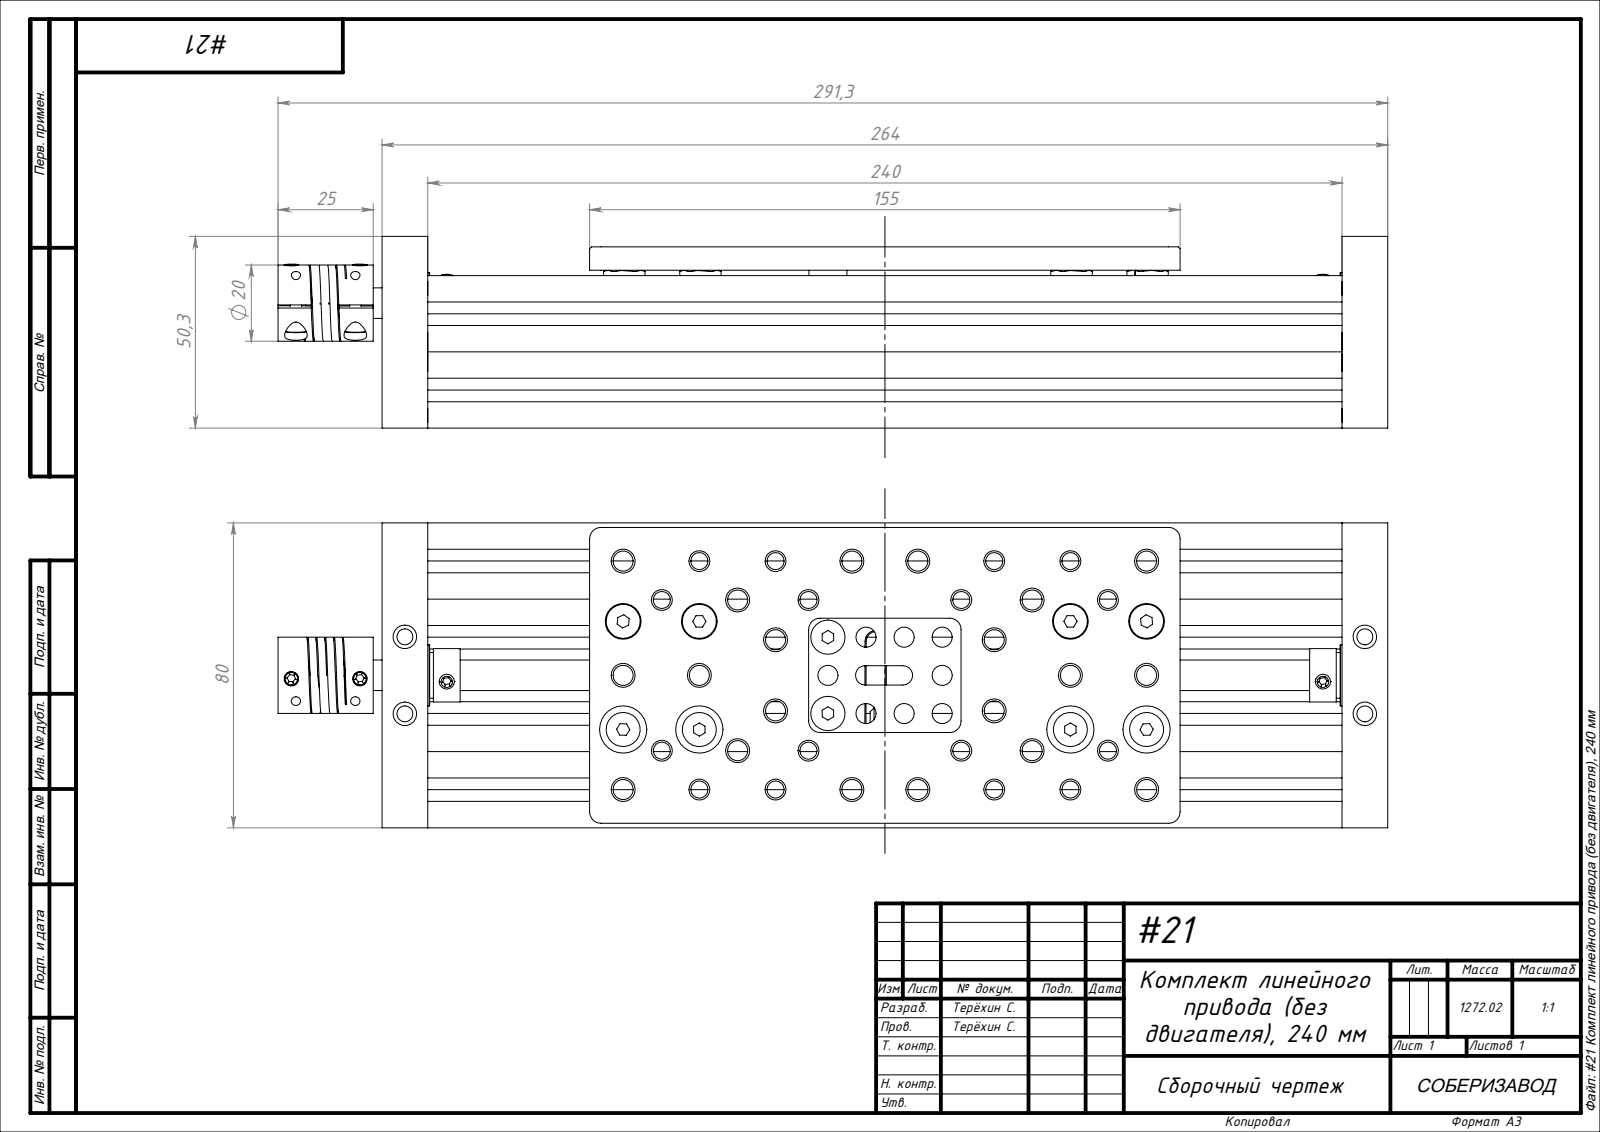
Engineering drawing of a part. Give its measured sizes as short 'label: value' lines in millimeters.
name: A137 Высокоточная прокладка O 5,3 O 8; Гайка М5, низкая DIN 439, K32_00; A225 Гибкая муфта O 6,35 O 8_00; Ì3õ10 DIN 912_M3(12) (+8 more)
written by: SolidWorks 2021 (AUTOMOTIVE_DESIGN)
unit: mm
bodies: 171 solids, 4603 faces (1282 planar, 1432 cylindrical, 1889 other)
size: 291.3 × 80 × 50.3
volume: 425 830 mm³; area: 308 895 mm²
holes: 42× ⌀5.3, 16× ⌀4.5, 16× ⌀5, 11× ⌀4.2, 10× ⌀4.13, 10× ⌀5.15, 8× ⌀6.09, 8× ⌀7.8, 8× ⌀8.4, 8× ⌀8.65, 4× ⌀5.2, 4× ⌀7.2
bosses: 12× ⌀8, 10× ⌀7.83, 8× ⌀15.23, 8× ⌀8.95, 8× ⌀8.64, 8× ⌀7, 8× ⌀6.27, 8× ⌀6
rounds: 100× R0.25, 86× R0.2, 48× R2, 40× R1, 30× R0.3, 20× R1.4, 8× R3, 6× R1.5
face distances: 14.14, 28.28, 12, 20, 1.8, 6, 12.34, 14, 42.42, 2.83
hole spacings: 20, 10, 22.39, 53.91, 6.2, 20.03, 22.37, 28.31
